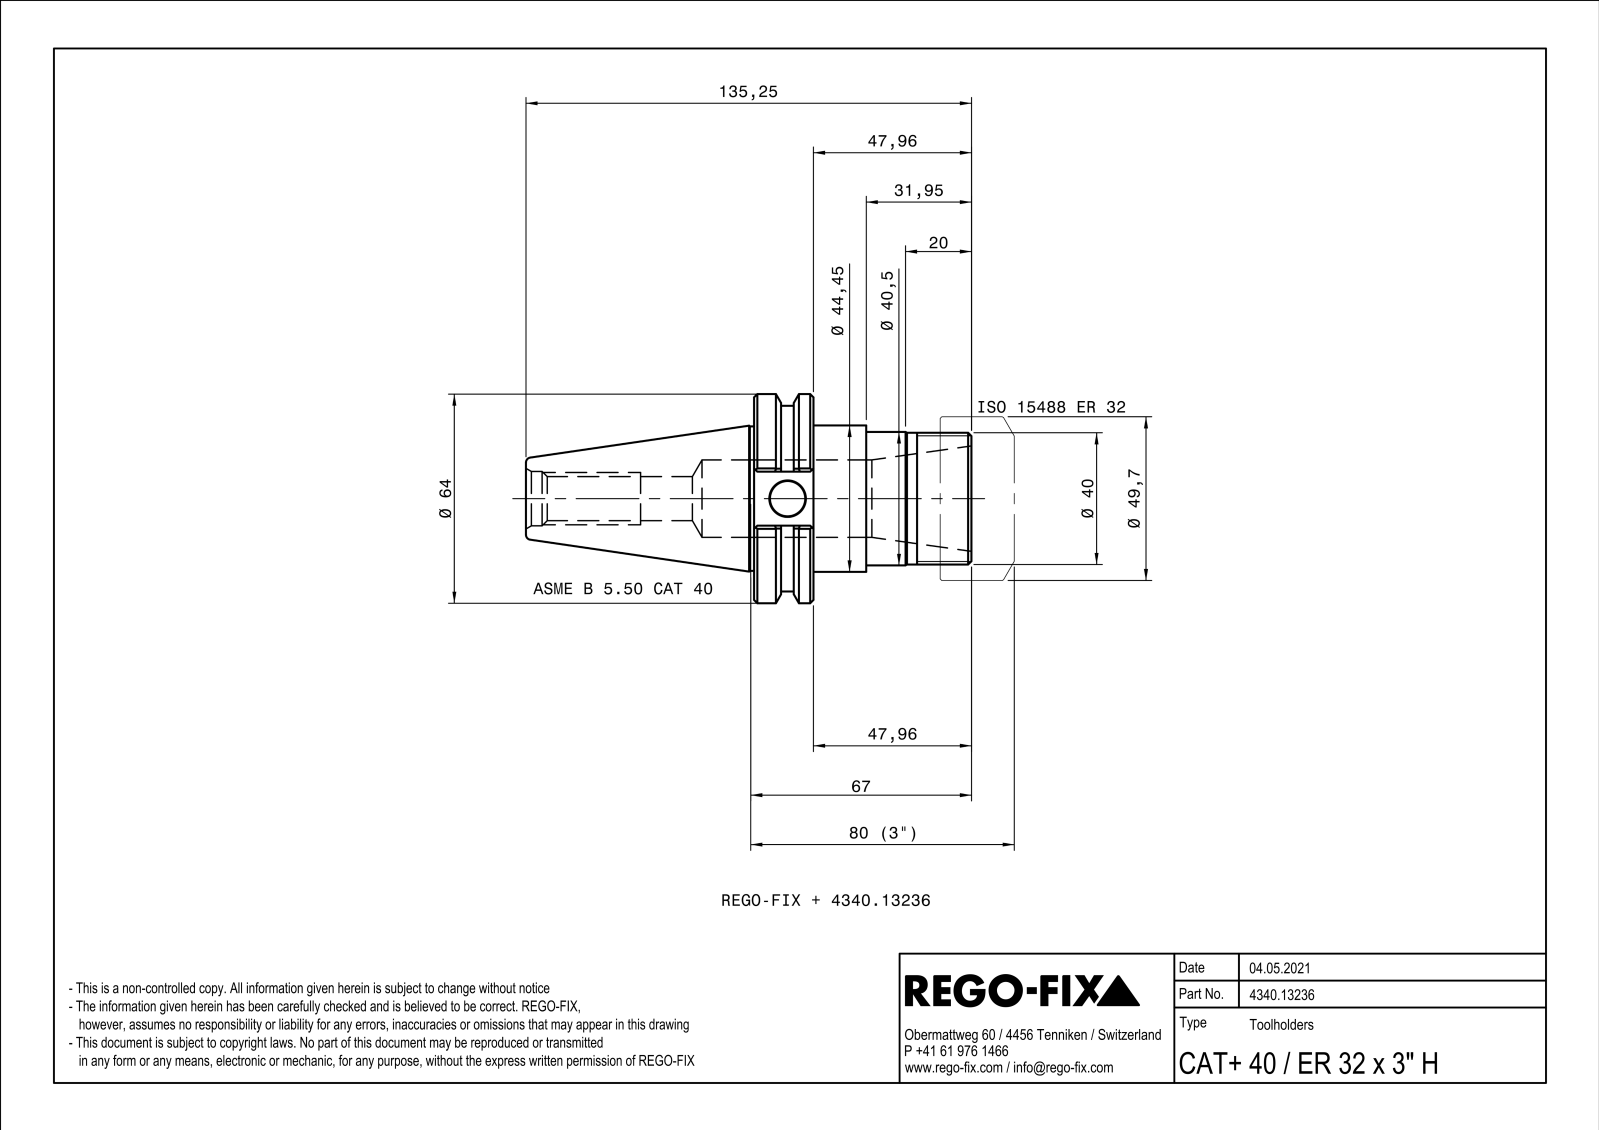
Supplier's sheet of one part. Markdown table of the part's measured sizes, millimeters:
| quantity | value |
| --- | --- |
| part name | NOCUT |
| STEP written by | SIEMENS PLM Software Solid Edge ST10 (AUTOMOTIVE_DESIGN) |
| units | millimeters |
| bodies | 2 solids, 215 faces (70 planar, 59 cylindrical, 86 other) |
| overall size | 135.65 × 63.8 × 61.04 |
| volume | 266 021 mm³ |
| surface area | 63 345 mm² |
| round holes (diameter × count) | 3.9 × 2, 3.24 × 1, 12 × 1, 13.38 × 1, 16.2 × 1, 16.5 × 1, 23.5 × 1 |
| round bosses / shafts (diameter × count) | 63.8 × 1, 63.5 × 1, 56.36 × 1, 44.75 × 1, 44.45 × 1, 43.85 × 1, 40.8 × 1, 40.5 × 1 |
| partial cylindrical surfaces (radius × count) | 0.5 × 4, 2.25 × 2 |
| main face-to-face distances | 18.05, 18.25, 66.2, 47.33, 48.15, 66.4, 47.95, 66, 16.38, 135.45 |
